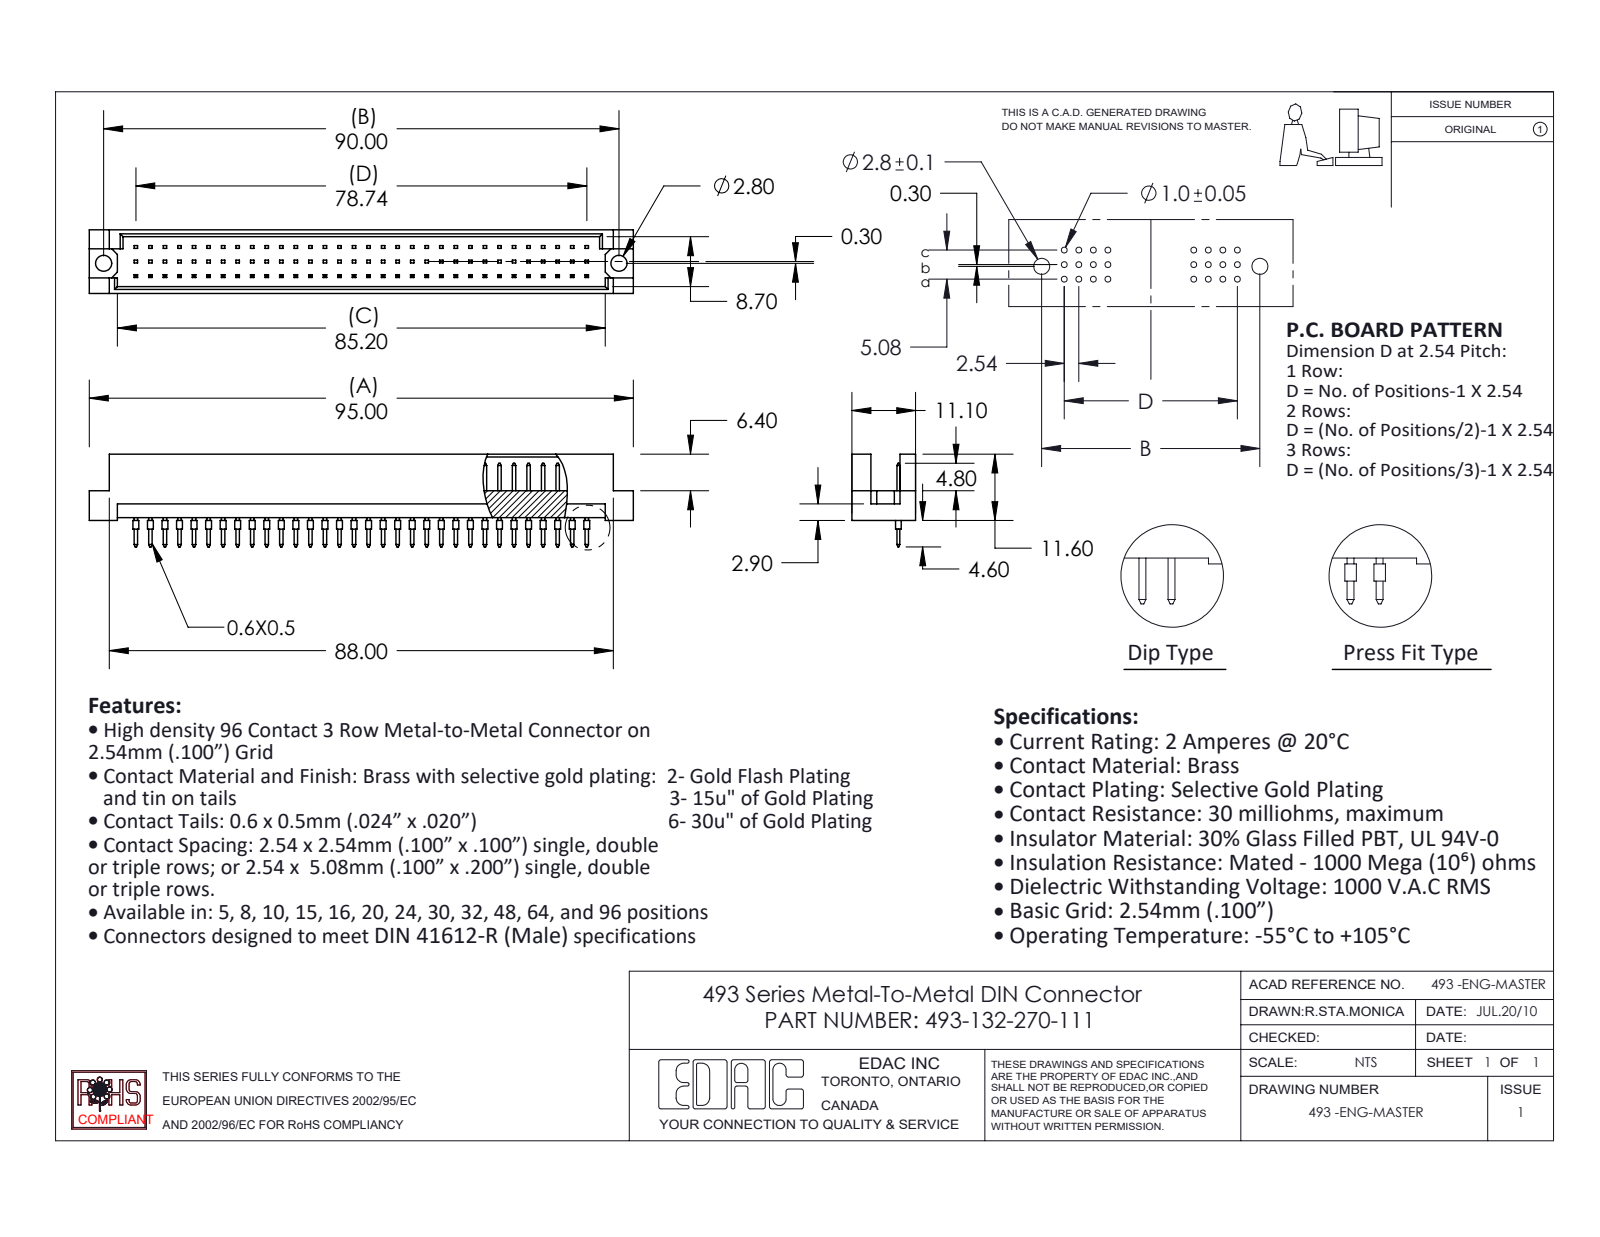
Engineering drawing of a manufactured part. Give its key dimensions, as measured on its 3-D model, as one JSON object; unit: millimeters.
{"part_name": "493 Part_96; 493-290_70; 493-132-270-111", "step_written_by": "SolidWorks 2020 (CONFIG_CONTROL_DESIGN)", "units": "millimeters", "bodies": {"solids": 33, "faces": 1140, "planar": 1072, "cylindrical": 68, "other": 0}, "overall_size": [95, 16.2, 11.1], "volume_mm3": 5819, "surface_area_mm2": 7566, "round_holes": [[2.8, 2]], "round_bosses_or_shafts": [[1, 32]], "face_to_face_distances": [1.2, 9.9, 11.1, 8.7, 4.7, 0.5, 2.54, 2.76, 8.34, 1.56], "hole_center_spacings": [90]}
